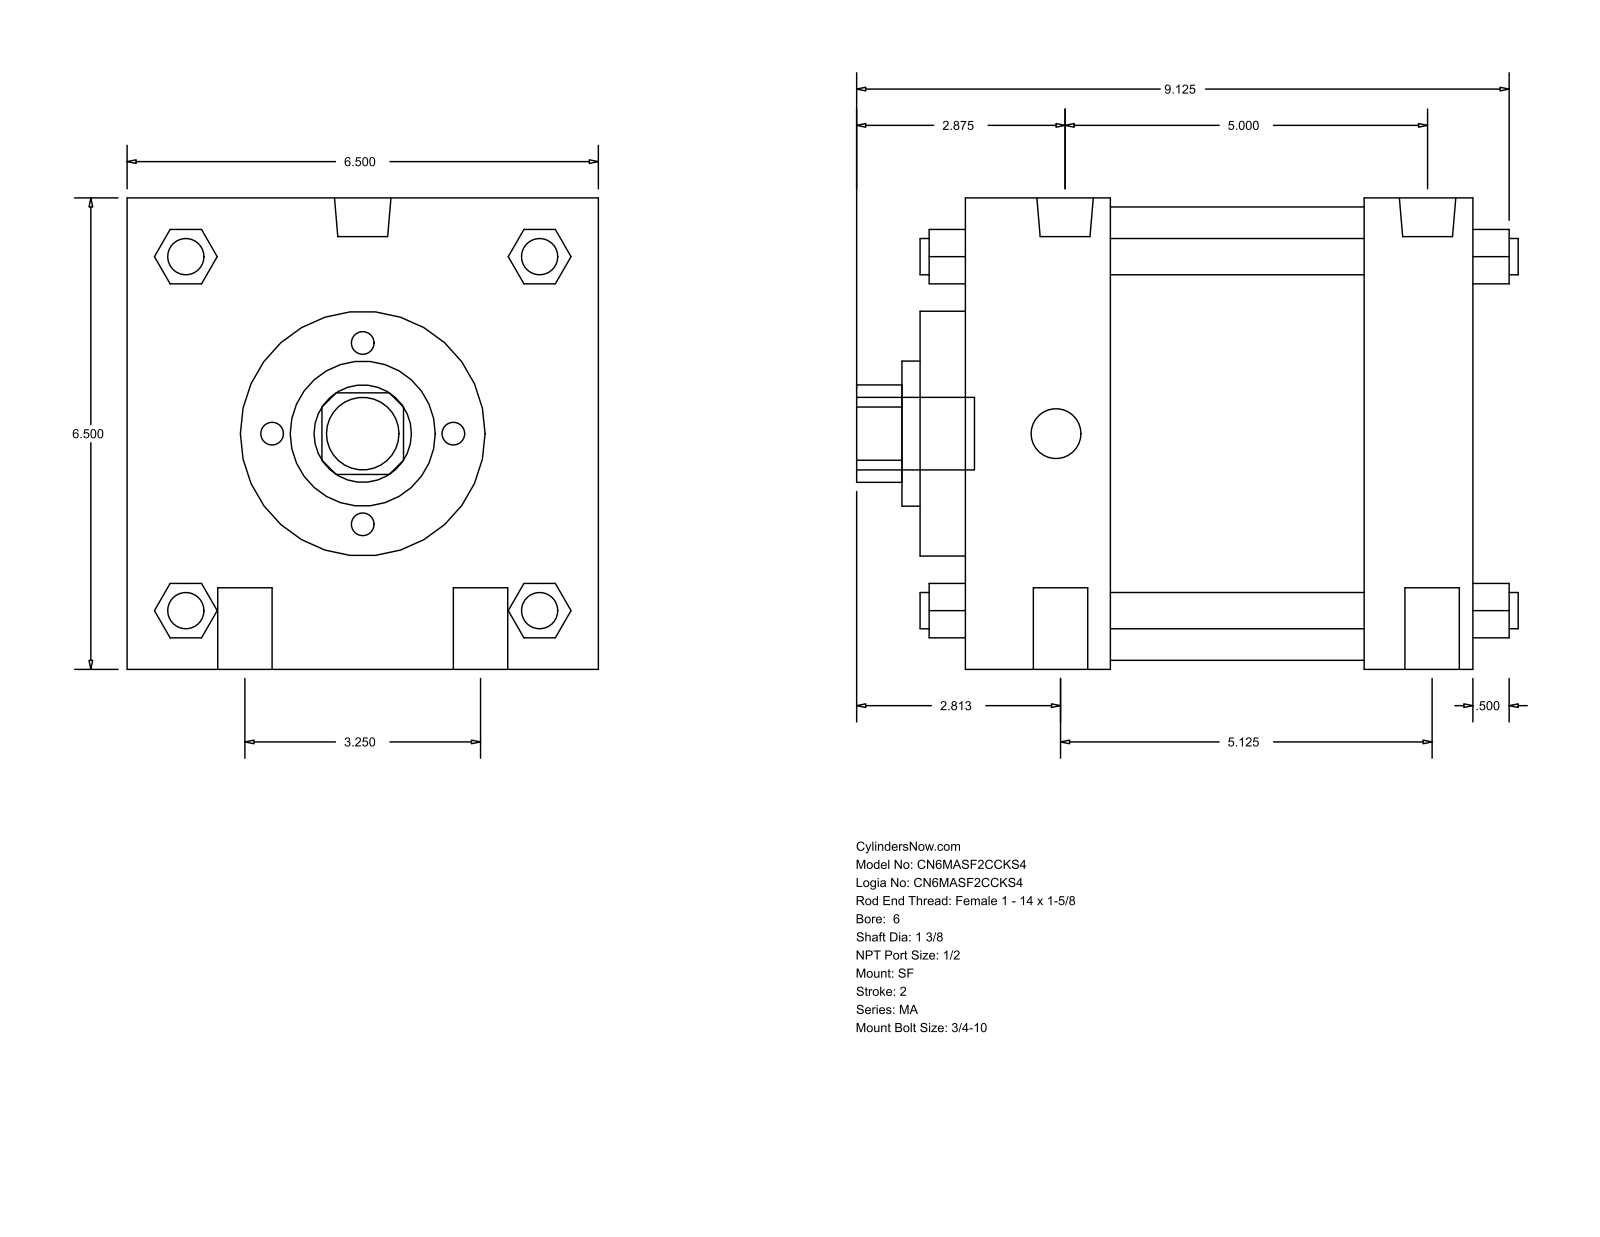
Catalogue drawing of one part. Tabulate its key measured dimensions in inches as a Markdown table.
| quantity | value |
| --- | --- |
| part name | MA_SF__0600_1.375 |
| STEP written by | GSSL Pune (CONFIG_CONTROL_DESIGN) |
| units | inches |
| bodies | 0 solids, 126 faces (95 planar, 31 cylindrical, 0 other) |
| overall size | 9.125 × 6.5 × 6.5 |
| round holes (diameter × count) | 1.375 × 1, 2 × 1, 3.375 × 1, 6.25 × 1 |
| round bosses / shafts (diameter × count) | 0.75 × 4, 0.5 × 4, 0.778 × 2, 0.687 × 2, 1 × 1 |
| partial cylindrical surfaces (radius × count) | 0.672 × 1 |
| main face-to-face distances | 6.5, 7, 5.5, 2, 1.5, 3.5, 5, 0.625, 2.625, 6.125 |
